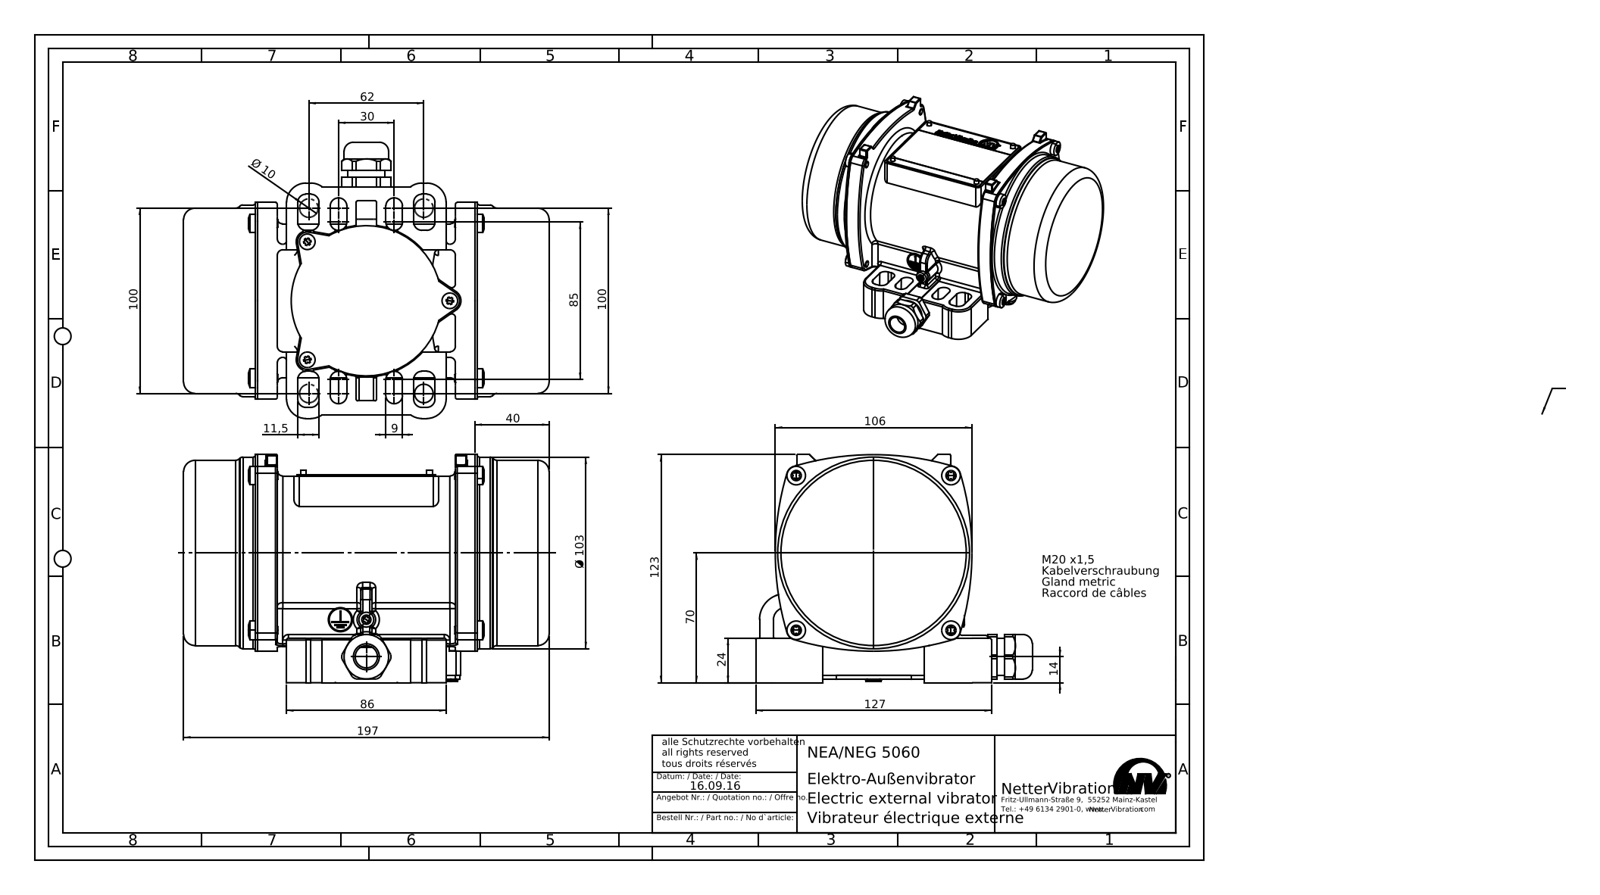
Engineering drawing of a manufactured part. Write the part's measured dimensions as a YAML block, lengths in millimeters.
part_name: "NEA-NEG 5060"
step_written_by: "SolidWorks 2015 (AUTOMOTIVE_DESIGN)"
units: millimeters
bodies: {solids: 20, faces: 2289, planar: 1075, cylindrical: 644, other: 570}
overall_size: [197, 149, 123]
volume: 474003
surface_area: 259272
round_holes:
  - {diameter: 3.4, count: 4}
  - {diameter: 4.5, count: 4}
  - {diameter: 6, count: 4}
  - {diameter: 12, count: 2}
  - {diameter: 13.5, count: 1}
  - {diameter: 14.5, count: 1}
  - {diameter: 17.5, count: 1}
  - {diameter: 69, count: 1}
  - {diameter: 78, count: 1}
  - {diameter: 97.5, count: 1}
  - {diameter: 101, count: 1}
round_bosses_or_shafts:
  - {diameter: 10, count: 4}
  - {diameter: 5, count: 4}
  - {diameter: 4, count: 4}
  - {diameter: 3, count: 4}
  - {diameter: 8.4, count: 3}
  - {diameter: 103.4, count: 1}
  - {diameter: 99.9, count: 1}
  - {diameter: 97, count: 1}
partial_cylinders:
  - {radius: 0.5, count: 63}
  - {radius: 1, count: 49}
  - {radius: 2, count: 28}
  - {radius: 3, count: 12}
  - {radius: 1.5, count: 9}
  - {radius: 10.5, count: 8}
  - {radius: 4.5, count: 5}
  - {radius: 5, count: 5}
face_to_face_distances: [1.2, 195.8, 2, 38.8, 157, 106.5, 40, 50.5, 155.8, 10.5]
hole_center_spacings: [44.05, 59, 83.44, 45, 4.4, 30.08, 56, 59.86]
